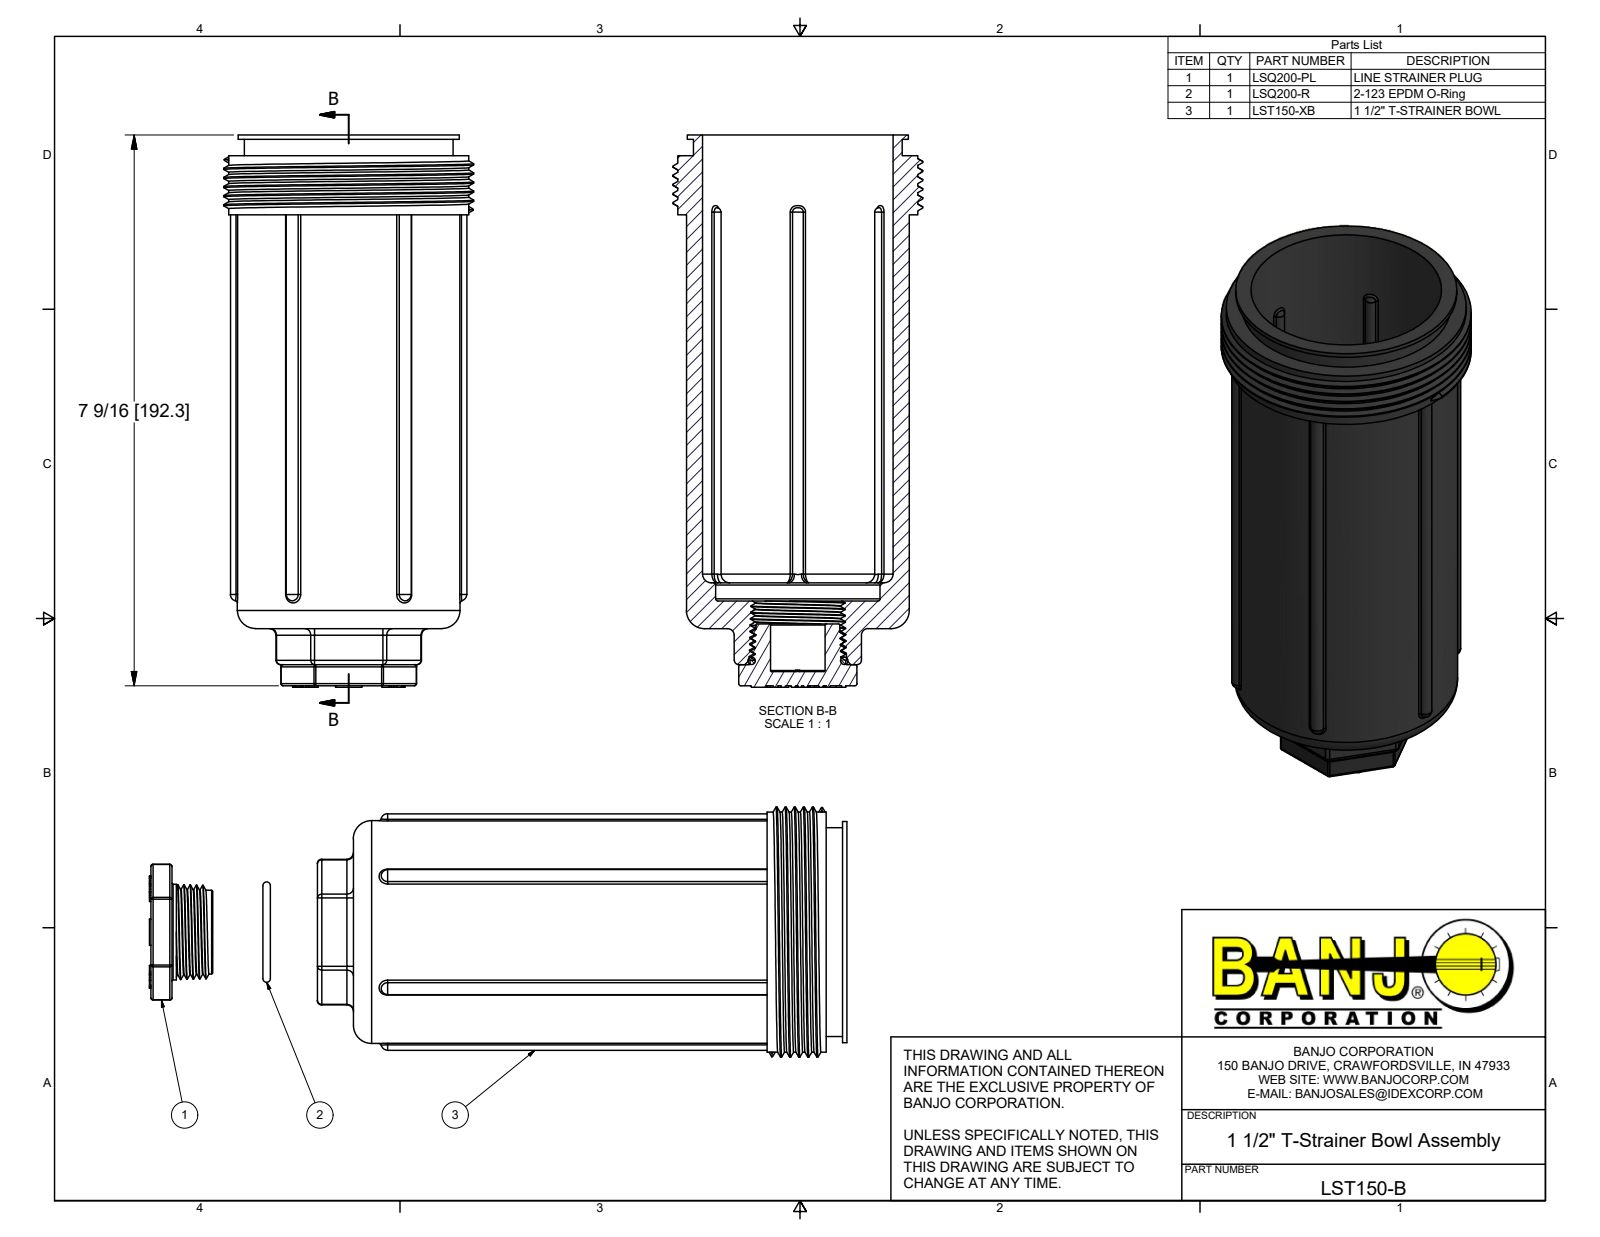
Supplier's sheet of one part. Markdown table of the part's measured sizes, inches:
| quantity | value |
| --- | --- |
| part name | LST150-B; LST150-XB; LSQ200-R; LSQ200-PL |
| STEP written by | Autodesk Inventor 2018 (AUTOMOTIVE_DESIGN) |
| units | inches |
| bodies | 3 solids, 684 faces (289 planar, 92 cylindrical, 303 other) |
| overall size | 7.59 × 3.436 × 3.436 |
| volume | 18.7 in³ |
| surface area | 164.5 in² |
| round holes (diameter × count) | 0.75 × 1, 2.26 × 1, 2.62 × 1 |
| round bosses / shafts (diameter × count) | 3.435 × 1, 3.3 × 1, 3.063 × 1, 3.04 × 1, 2.87 × 1, 1.315 × 1 |
| partial cylindrical surfaces (radius × count) | 0.03 × 42, 0.06 × 12, 0.078 × 6, 0.09 × 6, 0.094 × 6 |
| main face-to-face distances | 6.12, 0.38, 6.5, 6.785, 6.405, 0.285, 0.785, 1.165, 7.285, 7.57 |
